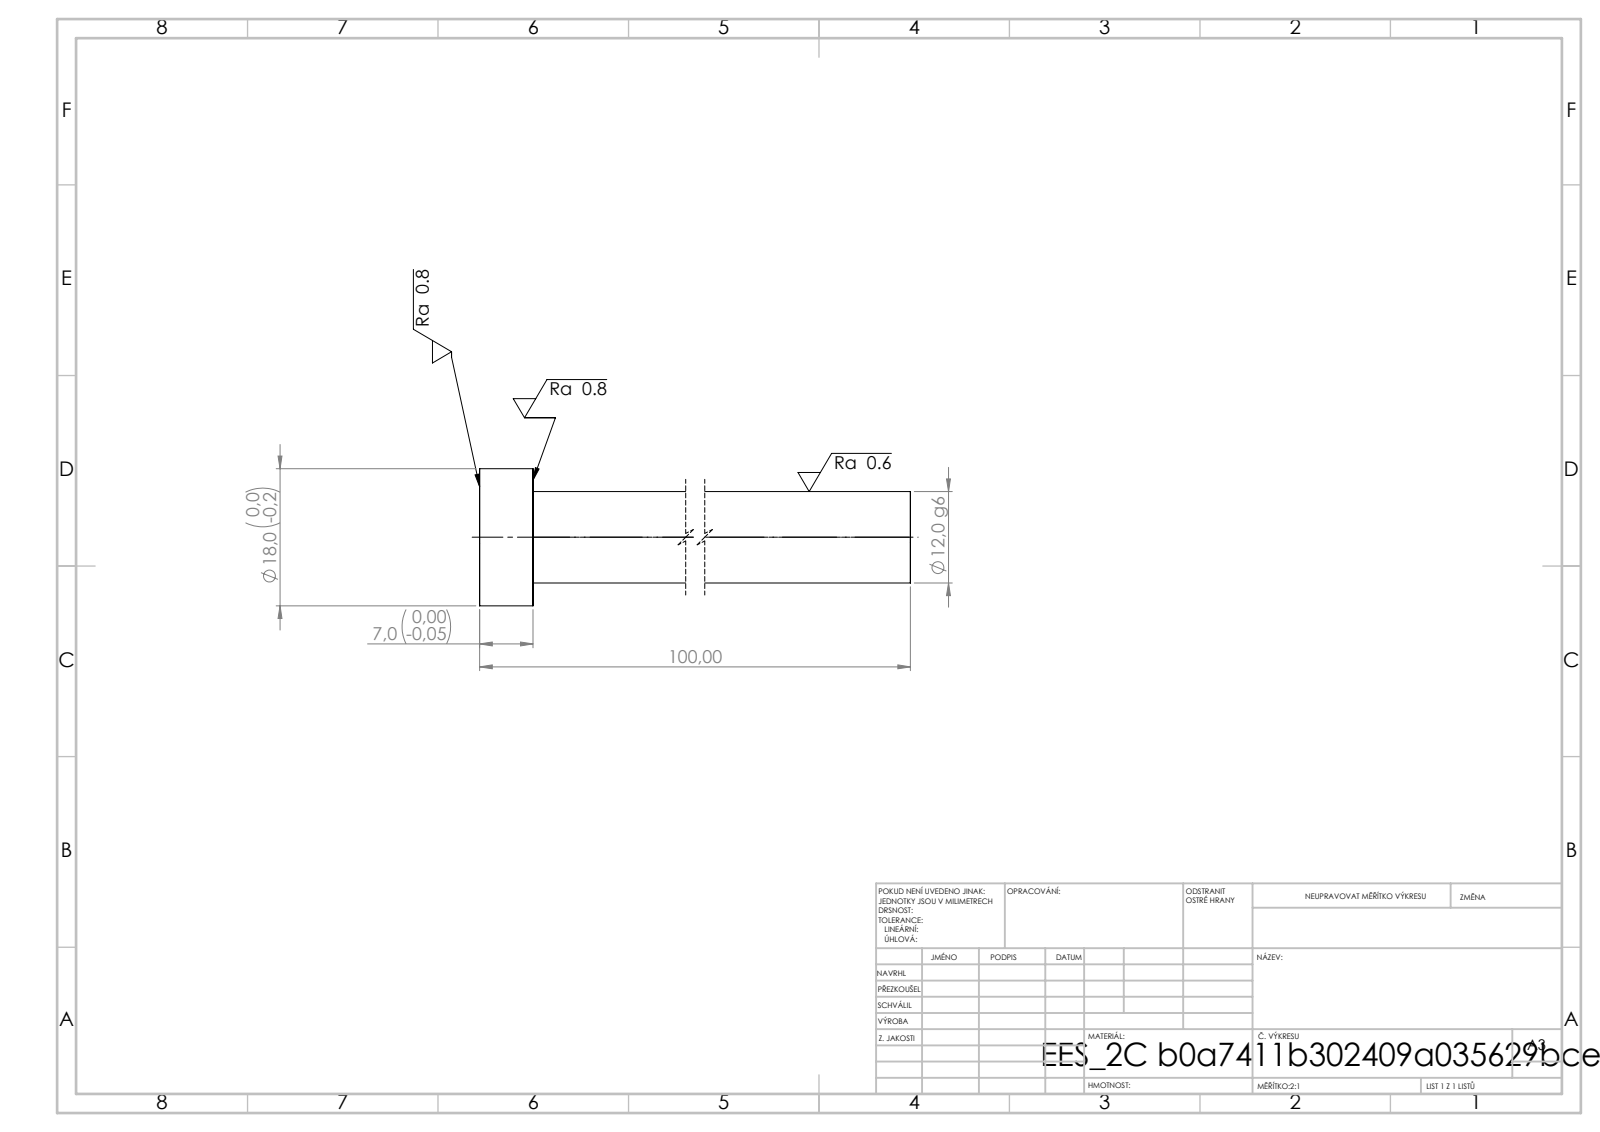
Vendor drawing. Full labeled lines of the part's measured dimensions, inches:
STEP written by: SolidWorks 2019 (CONFIG_CONTROL_DESIGN)
Units: inches
Bodies: 1 solid, 7 faces (3 planar, 4 cylindrical, 0 other)
Overall size (bounding box): 3.937 × 0.709 × 0.709
Volume: 0.751 in³ · Surface area: 6.837 in²
Round bosses / shafts (diameter × count): ⌀0.709 ×1, ⌀0.472 ×1
Main face-to-face distances: 0.276, 3.937, 3.661
